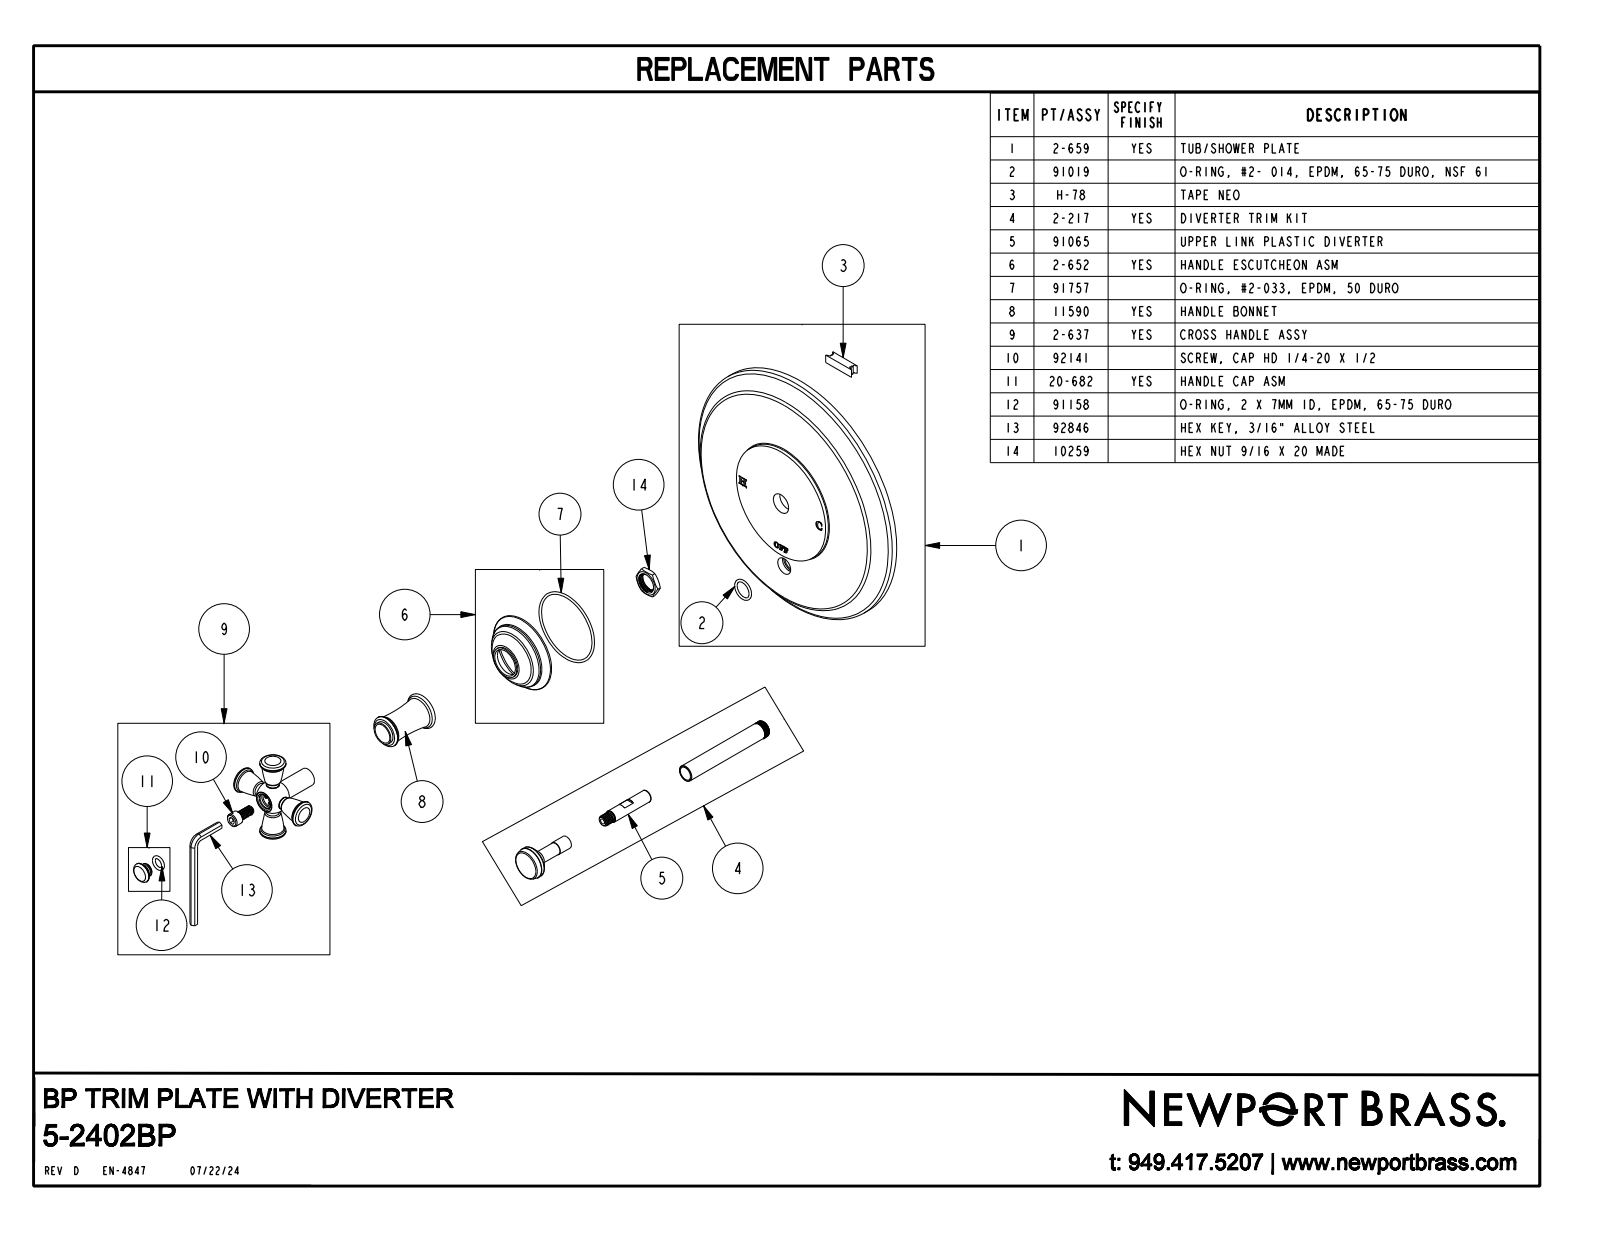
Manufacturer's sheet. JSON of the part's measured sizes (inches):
{"part_name": "5-2402BP", "step_written_by": "CREO PARAMETRIC BY PTC INC, 2018400 (CONFIG_CONTROL_DESIGN)", "units": "inches", "bodies": {"solids": 1, "faces": 291, "planar": 42, "cylindrical": 32, "other": 217}, "overall_size": [7.5, 7.5, 4.061], "volume_in3": 29.75, "surface_area_in2": 116.9, "round_bosses_or_shafts": [[0.9, 2], [0.72, 2], [0.36, 2], [7.5, 1], [0.649, 1], [0.56, 1], [0.517, 1], [0.472, 1]], "face_to_face_distances": [0.625, 0.75, 0.125, 1.977, 1.352, 1.227, 2.89, 2.265, 2.14, 0.913]}
